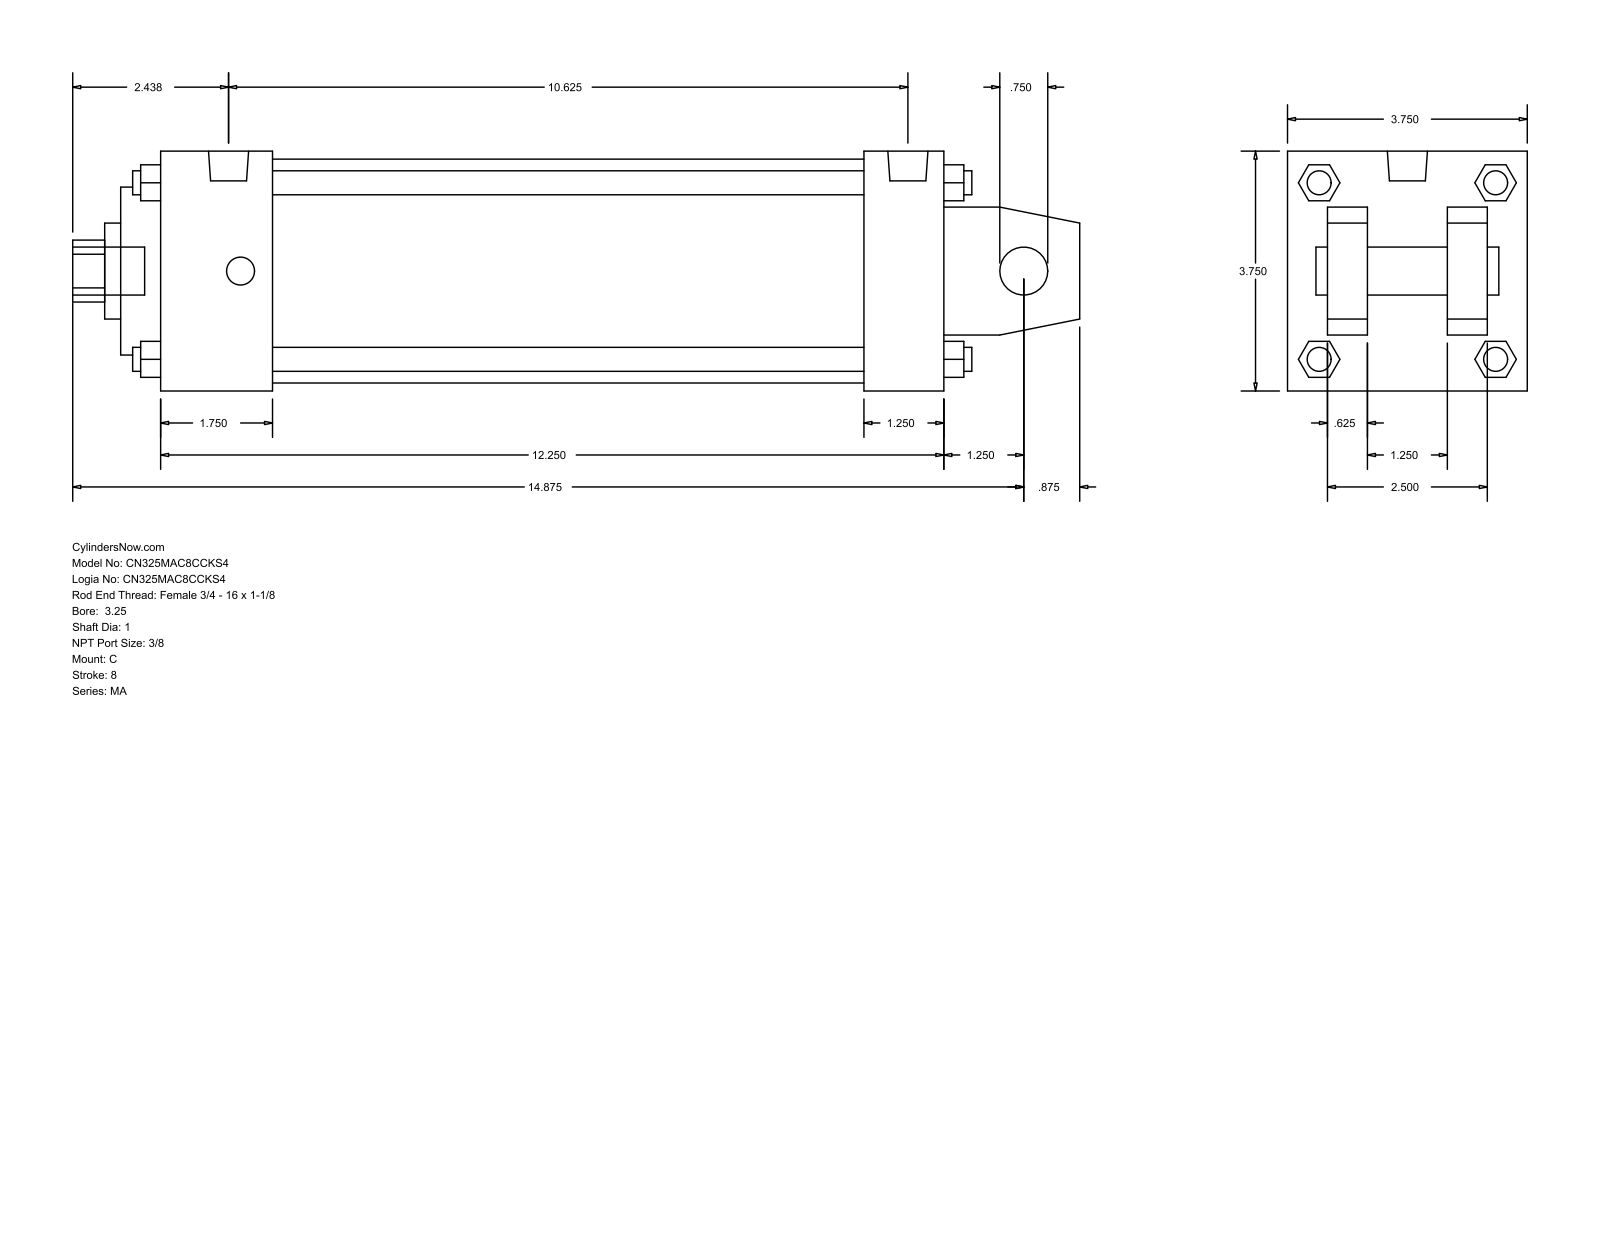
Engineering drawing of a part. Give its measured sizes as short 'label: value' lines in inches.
name: MA_C__0325_1
written by: GSSL Pune (CONFIG_CONTROL_DESIGN)
unit: in
bodies: 0 solids, 141 faces (109 planar, 32 cylindrical, 0 other)
size: 15.75 × 3.75 × 3.75
holes: 1× ⌀0.75, 1× ⌀1, 1× ⌀1.5, 1× ⌀2.625, 1× ⌀3.5
bosses: 4× ⌀0.437, 4× ⌀0.375, 2× ⌀0.627, 1× ⌀0.75
rounds: 1× R0.484
face distances: 3.75, 0.625, 2.5, 12.25, 1.25, 3.125, 1.875, 12.875, 11, 1.25
